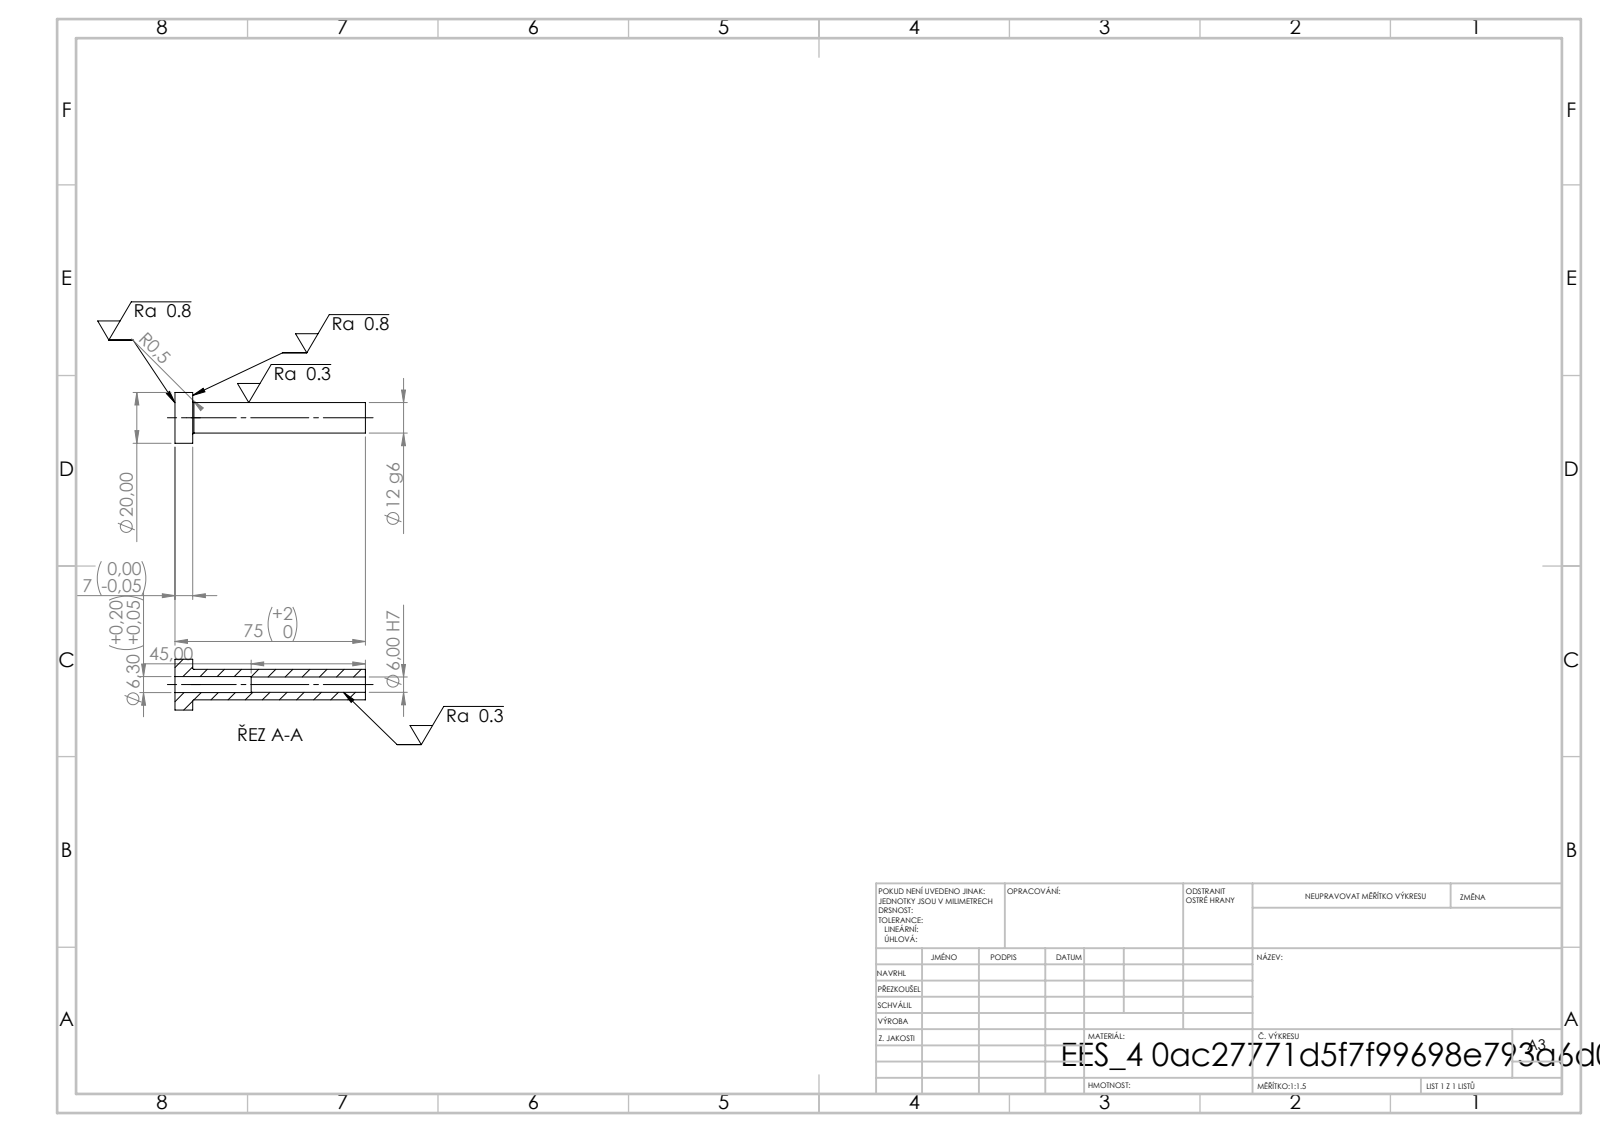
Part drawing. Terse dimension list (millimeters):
written by: SolidWorks 2019 (CONFIG_CONTROL_DESIGN)
unit: mm
bodies: 1 solid, 14 faces (4 planar, 8 cylindrical, 2 other)
size: 75 × 20 × 20
volume: 7 684 mm³; area: 5 009 mm²
holes: 1× ⌀6, 1× ⌀6.3
bosses: 1× ⌀20, 1× ⌀12
face distances: 7, 75, 68, 30, 23, 45
